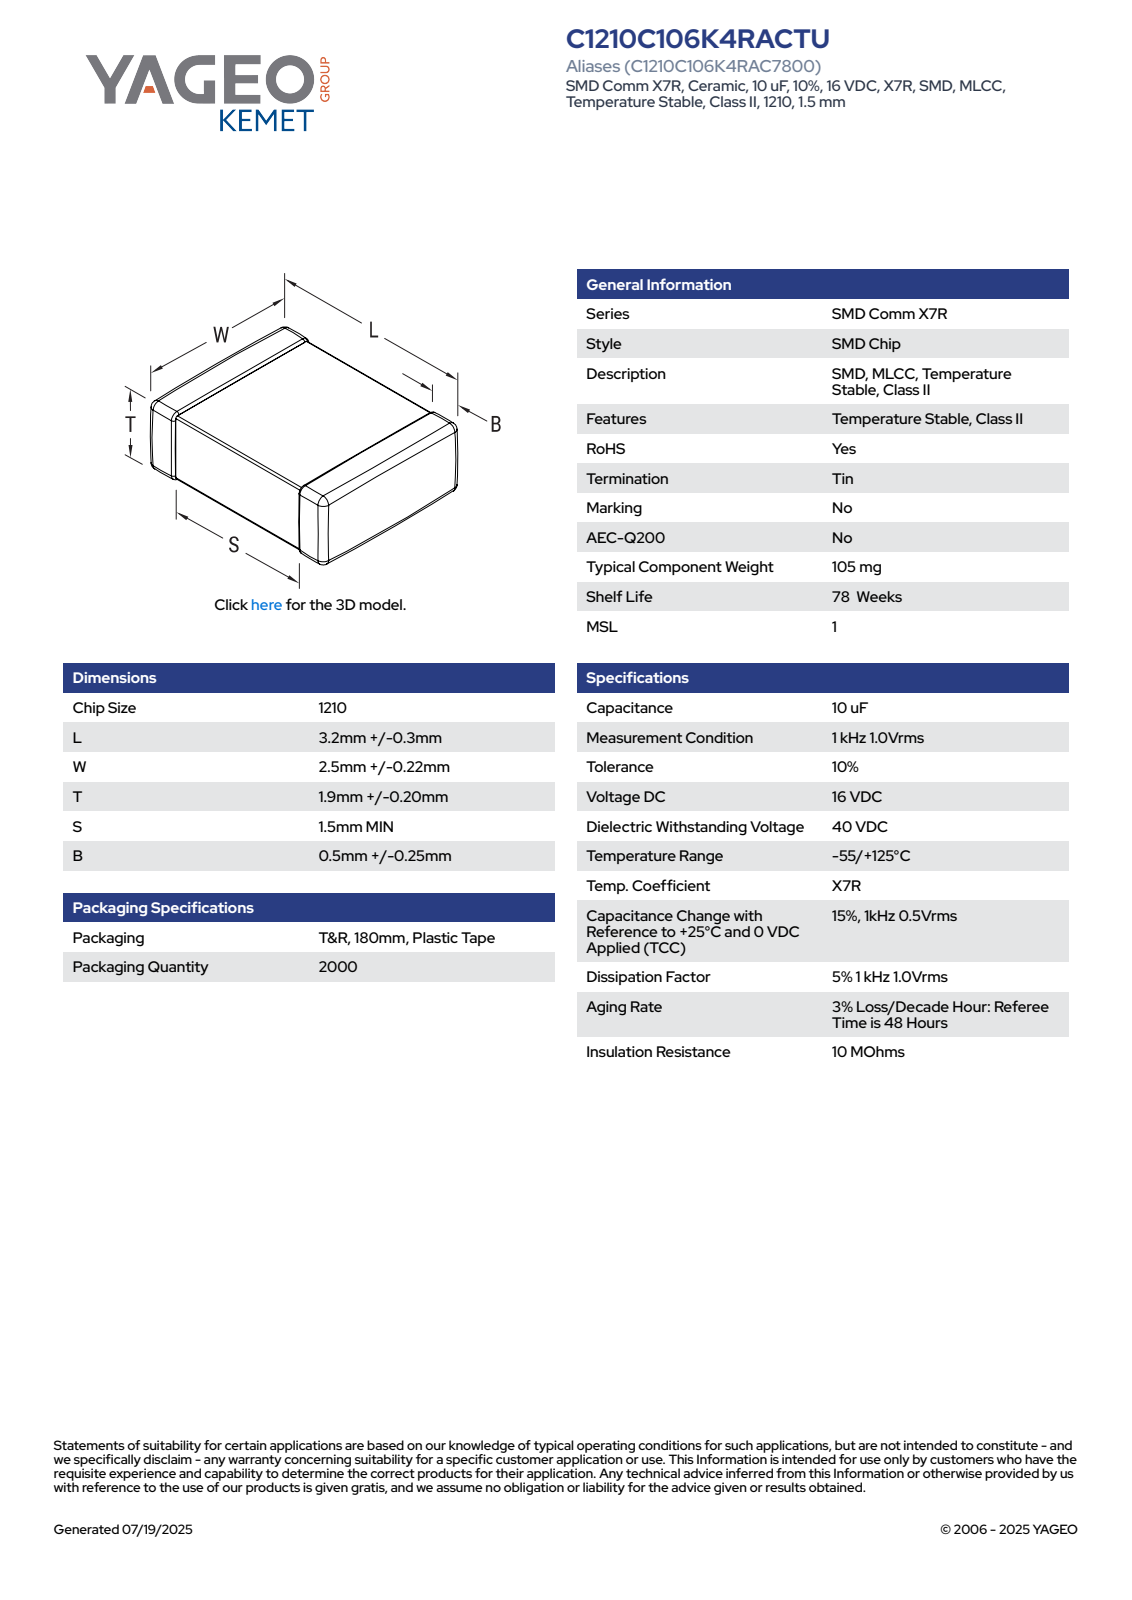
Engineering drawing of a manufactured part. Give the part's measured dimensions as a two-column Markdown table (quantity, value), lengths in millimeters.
| quantity | value |
| --- | --- |
| part name | CCS_CCSTD_1210_L3.5W2.72T2.1B0.5 |
| STEP written by | SolidWorks 2021 (AUTOMOTIVE_DESIGN) |
| units | millimeters |
| bodies | 4 solids, 125 faces (71 planar, 38 cylindrical, 16 other) |
| overall size | 3.5 × 2.72 × 2.1 |
| volume | 19 mm³ |
| surface area | 45 mm² |
| main face-to-face distances | 2.04, 3.5, 2.66, 1.98, 2.6, 2.1, 2.72, 2.05, 1.99, 1.49 |
